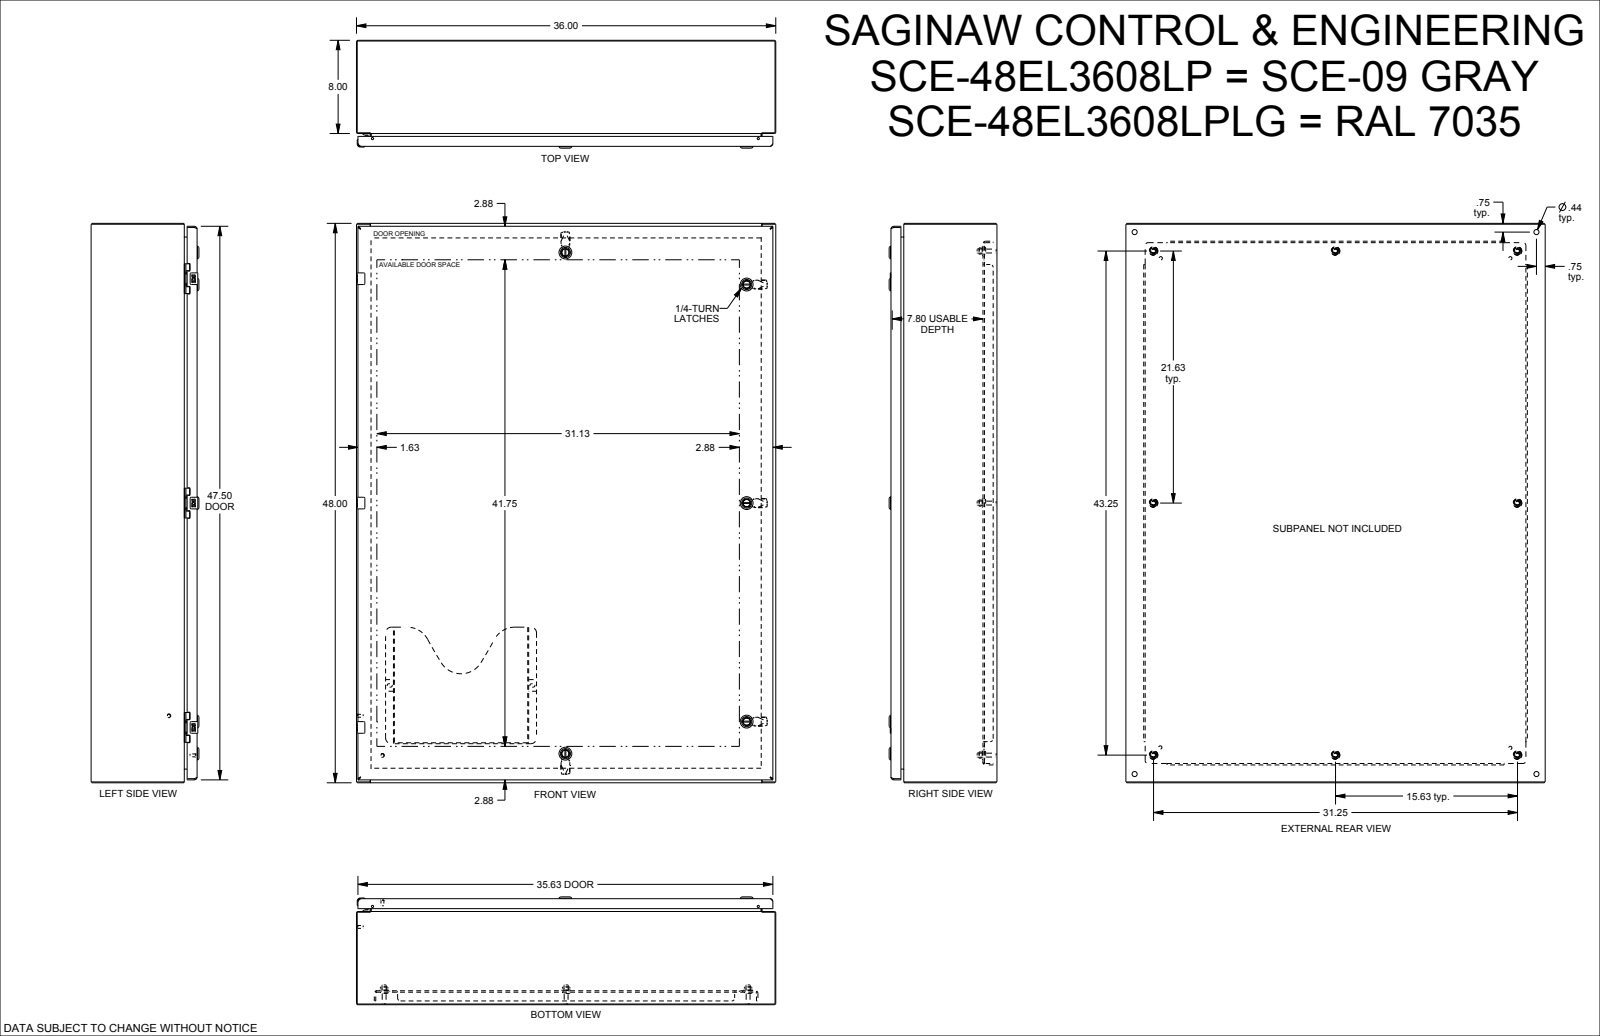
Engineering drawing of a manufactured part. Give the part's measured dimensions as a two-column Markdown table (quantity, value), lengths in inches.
| quantity | value |
| --- | --- |
| part name | SCE-48EL3608LPLG |
| STEP written by | SolidWorks 2019 (CONFIG_CONTROL_DESIGN) |
| units | inches |
| bodies | 0 solids, 4768 faces (2330 planar, 1319 cylindrical, 1119 other) |
| overall size | 48 × 36 × 9.256 |
| round holes (diameter × count) | 0.367 × 8, 0.5 × 8, 0.172 × 6, 0.205 × 6, 0.244 × 6, 0.266 × 6, 0.375 × 6, 0.197 × 5, 0.315 × 5, 0.394 × 5, 0.634 × 5, 0.281 × 4 |
| round bosses / shafts (diameter × count) | 0.17 × 9, 0.366 × 8, 0.332 × 8, 0.25 × 6, 0.24 × 6, 1.102 × 5, 0.866 × 5, 0.802 × 5 |
| partial cylindrical surfaces (radius × count) | 0.012 × 136, 0.01 × 52, 0.02 × 52, 0.015 × 32, 0.157 × 20, 0.04 × 17, 0.025 × 16, 0.1 × 16 |
| main face-to-face distances | 0.075, 0.104, 8.92, 8.995, 9.099, 9.024, 1.125, 7.795, 1, 7.92 |
| hole center spacings | 19.25, 38.5, 0.05, 0.493, 0.494, 0.986, 18.265, 18.757 |
